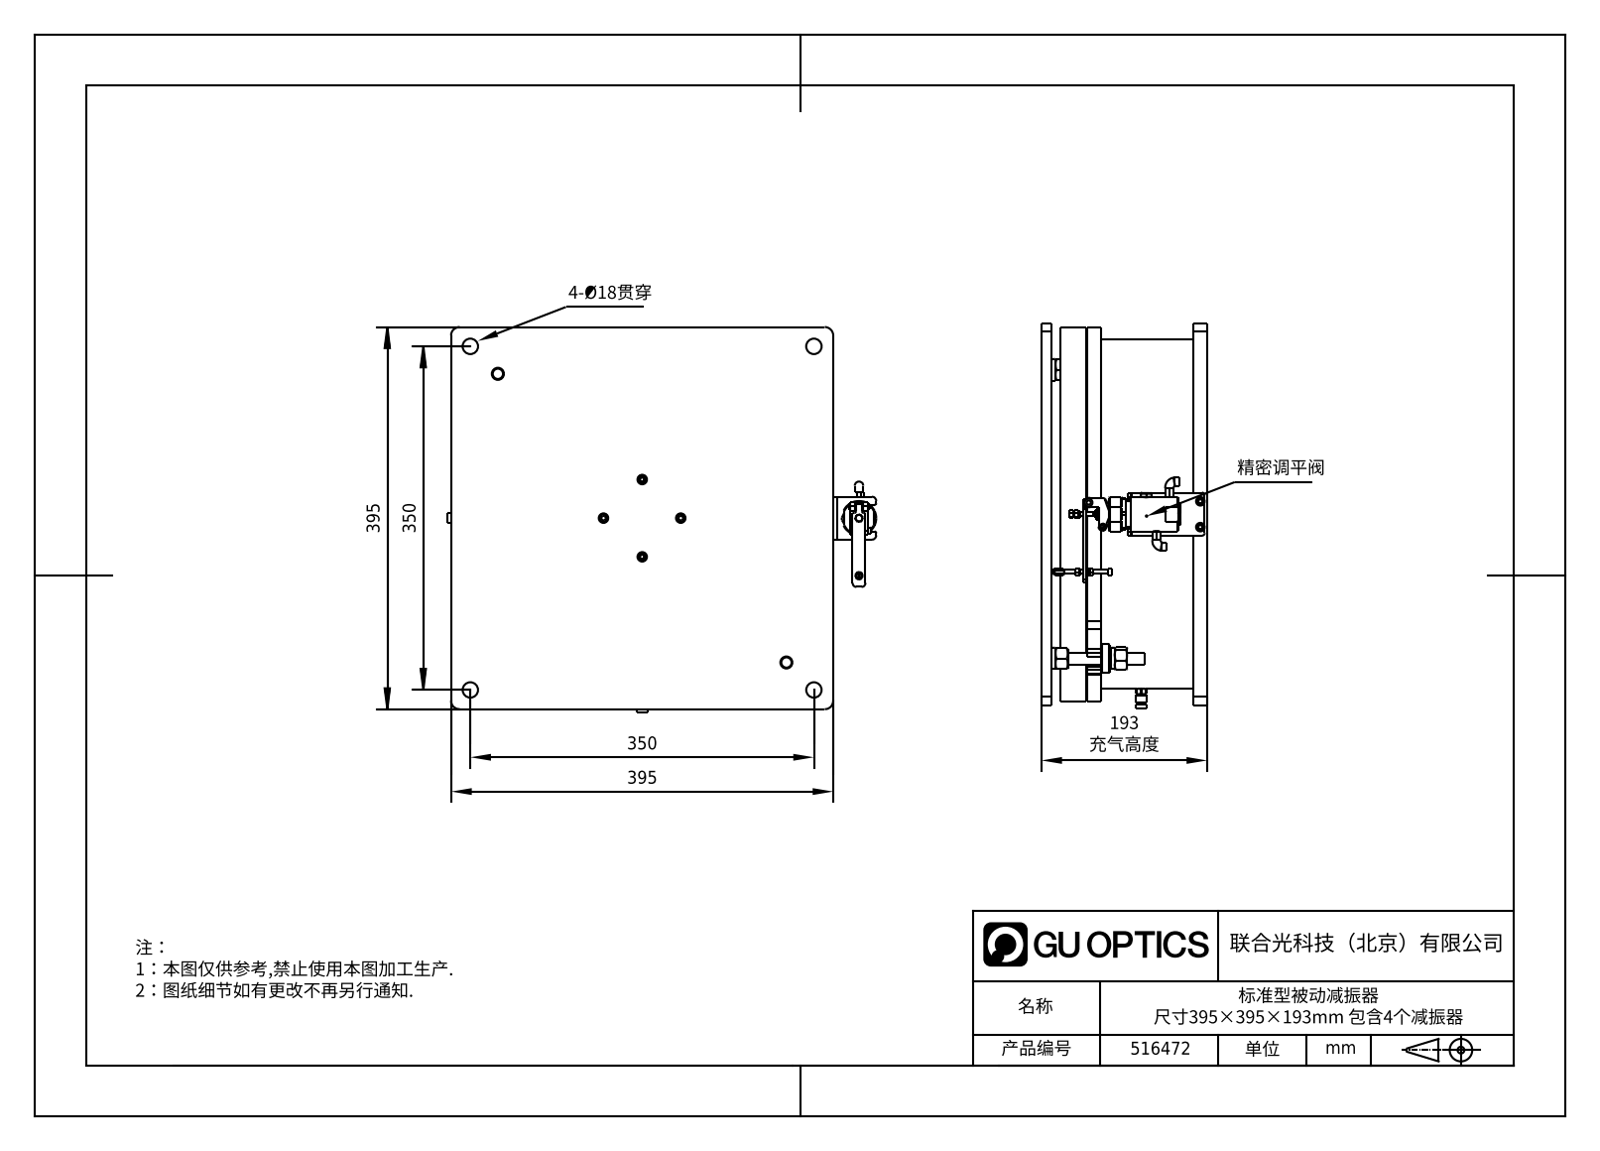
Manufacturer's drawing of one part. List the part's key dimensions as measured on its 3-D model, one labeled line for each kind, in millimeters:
Part name (STEP PRODUCT): 516472
STEP written by: SolidWorks 2020 (CONFIG_CONTROL_DESIGN)
Units: millimetres
Bodies: 0 solids, 450 faces (246 planar, 140 cylindrical, 64 other)
Overall size (bounding box): 448.8 × 398.8 × 193
Round holes (diameter × count): ⌀18 ×4, ⌀9.7 ×3, ⌀12.7 ×3, ⌀5 ×1, ⌀13 ×1, ⌀15 ×1, ⌀34 ×1, ⌀40 ×1, ⌀385 ×1
Round bosses / shafts (diameter × count): ⌀11 ×5, ⌀12 ×4, ⌀12.6 ×3, ⌀10.4 ×3, ⌀10 ×3, ⌀8.45 ×3, ⌀8.1 ×3, ⌀8 ×3
Partial cylindrical surfaces — rounded edges, fillets, slot ends (radius × count): R5 ×10, R10 ×8, R0.3 ×4, R2 ×3, R7 ×3, R3 ×2, R4.5 ×2, R11 ×2
Main face-to-face distances: 16, 12, 193, 177, 181, 165, 124, 57, 108, 69
Hole centre spacings: 247.49, 325.96, 350, 35.36, 38, 182.71, 189.8, 193.57
